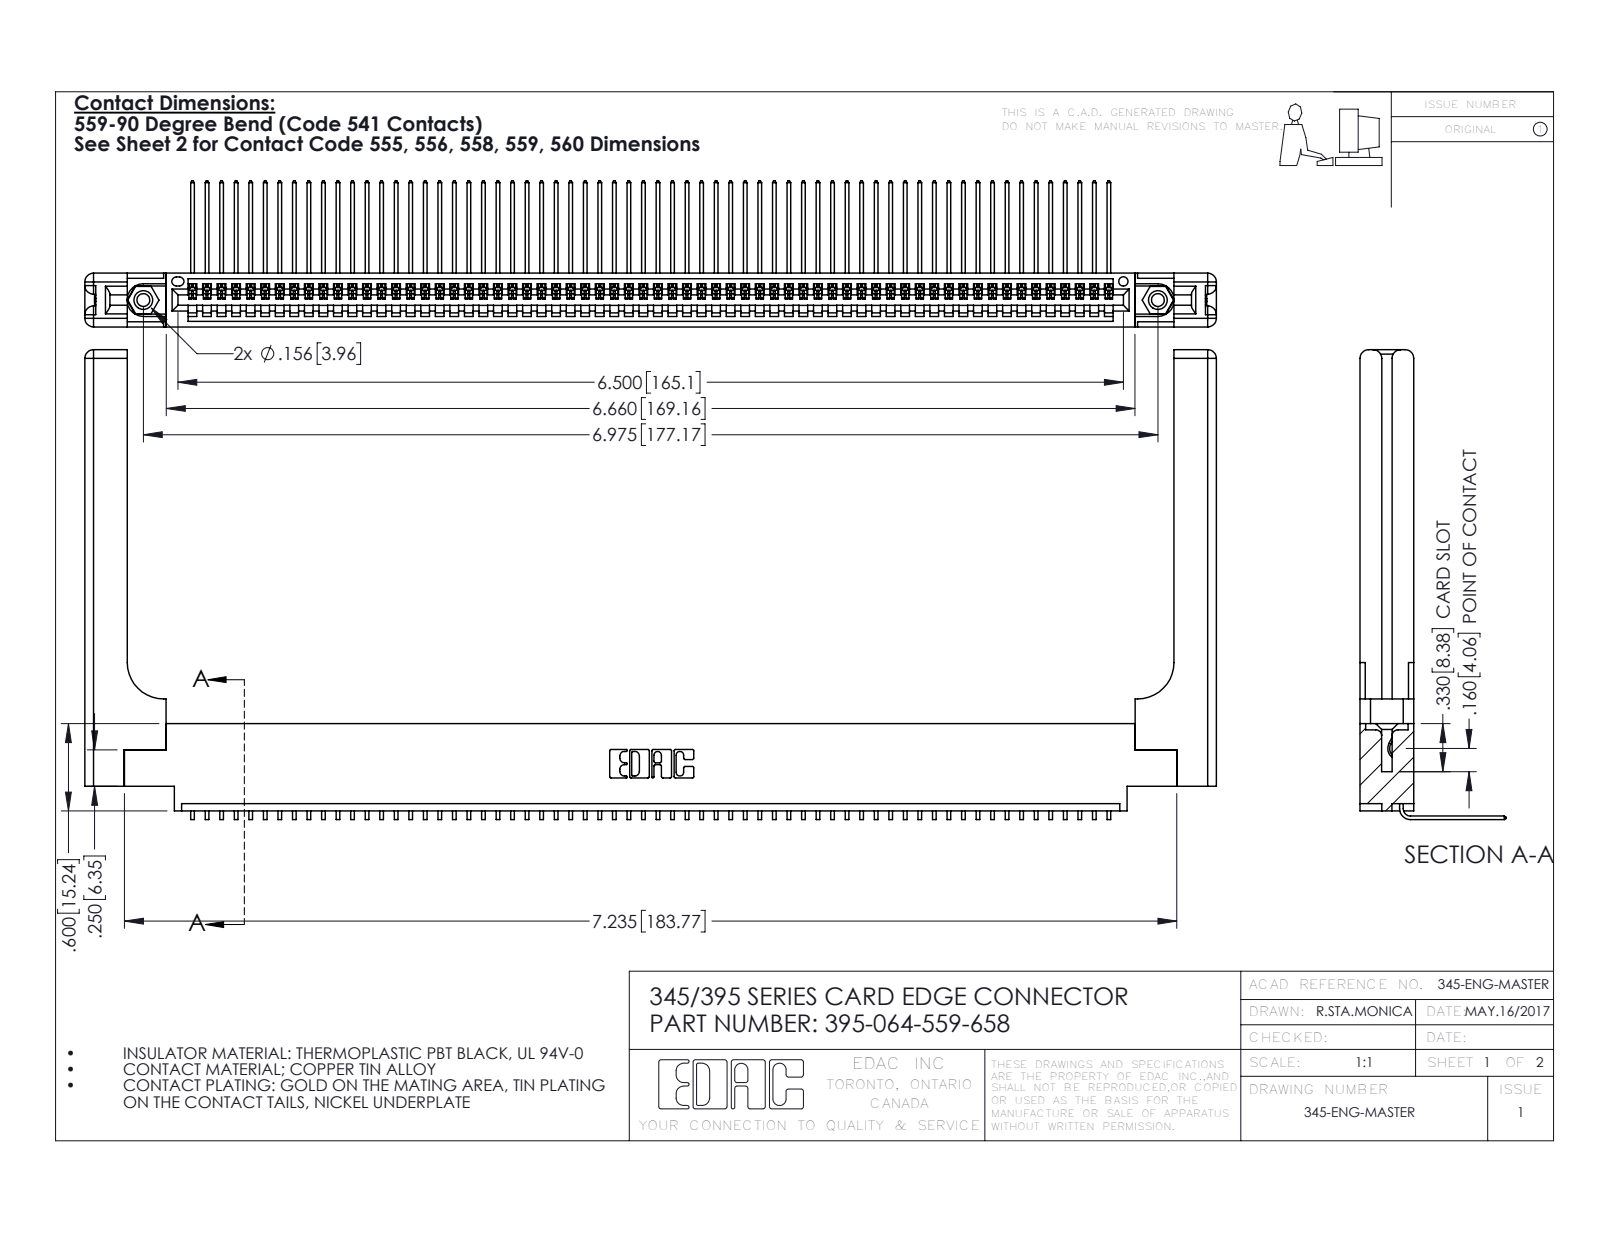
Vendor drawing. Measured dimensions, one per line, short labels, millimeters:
name: 345-292-001_558 559 Tail - 1; 345 Part_0.170 Offset - 0.156 Dia-TH; 345-220-058_345-220-058; 345-250-001_345-250-001-102 (+1 more)
written by: SolidWorks 2016 (CONFIG_CONTROL_DESIGN)
unit: mm
bodies: 69 solids, 4226 faces (2920 planar, 1246 cylindrical, 60 other)
size: 197.6 × 82 × 25.5
volume: 27 550 mm³; area: 32 300 mm²
holes: 2× ⌀2.3, 2× ⌀3.2, 2× ⌀4, 1× ⌀1.6
bosses: 2× ⌀3.9
rounds: 128× R0.2, 22× R0.3, 16× R1.5, 6× R0.2, 6× R0.8, 3× R0.7, 2× R0.8, 2× R0.8
face distances: 1.8, 9.4, 7.6, 2.5, 6.9, 0.6, 5.1, 5.7, 3.8, 3.8
hole spacings: 6.9, 171.2, 177.2
